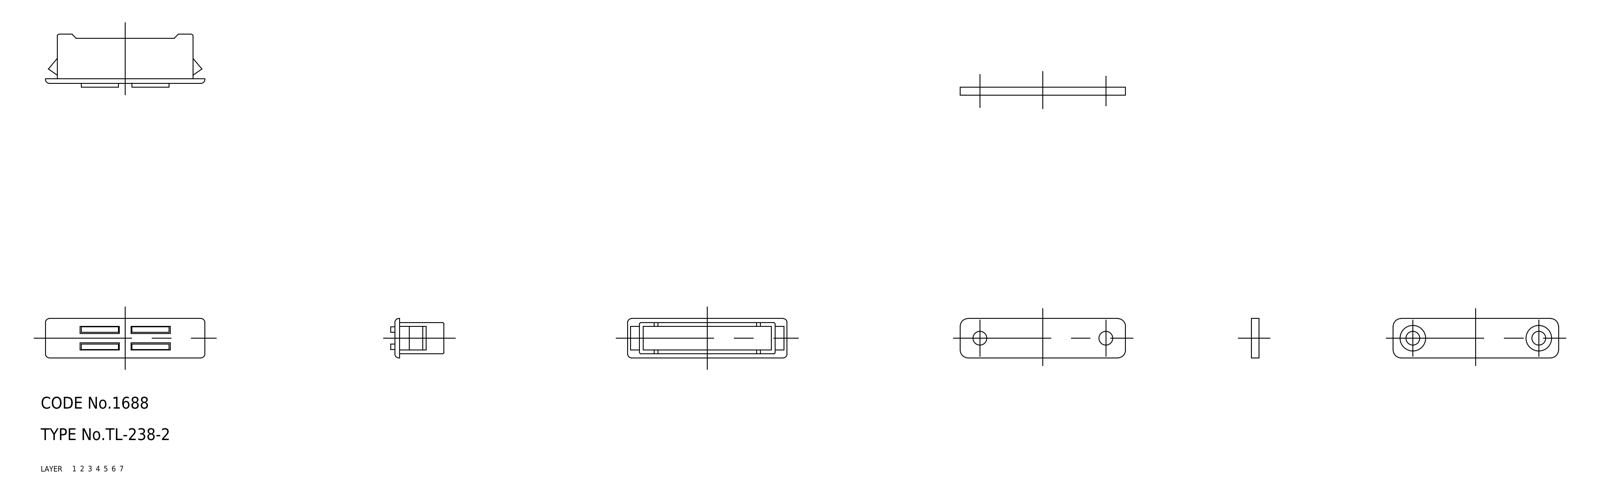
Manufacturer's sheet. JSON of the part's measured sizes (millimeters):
{"part_name": "attachment; keeper; housing; claw (+1 more)", "step_written_by": "CADfix (AUTOMOTIVE_DESIGN)", "units": "millimeters", "bodies": {"solids": 5, "faces": 116, "planar": 0, "cylindrical": 0, "other": 116}, "overall_size": [42, 34.1, 10], "volume_mm3": 3195, "surface_area_mm2": 5423}
